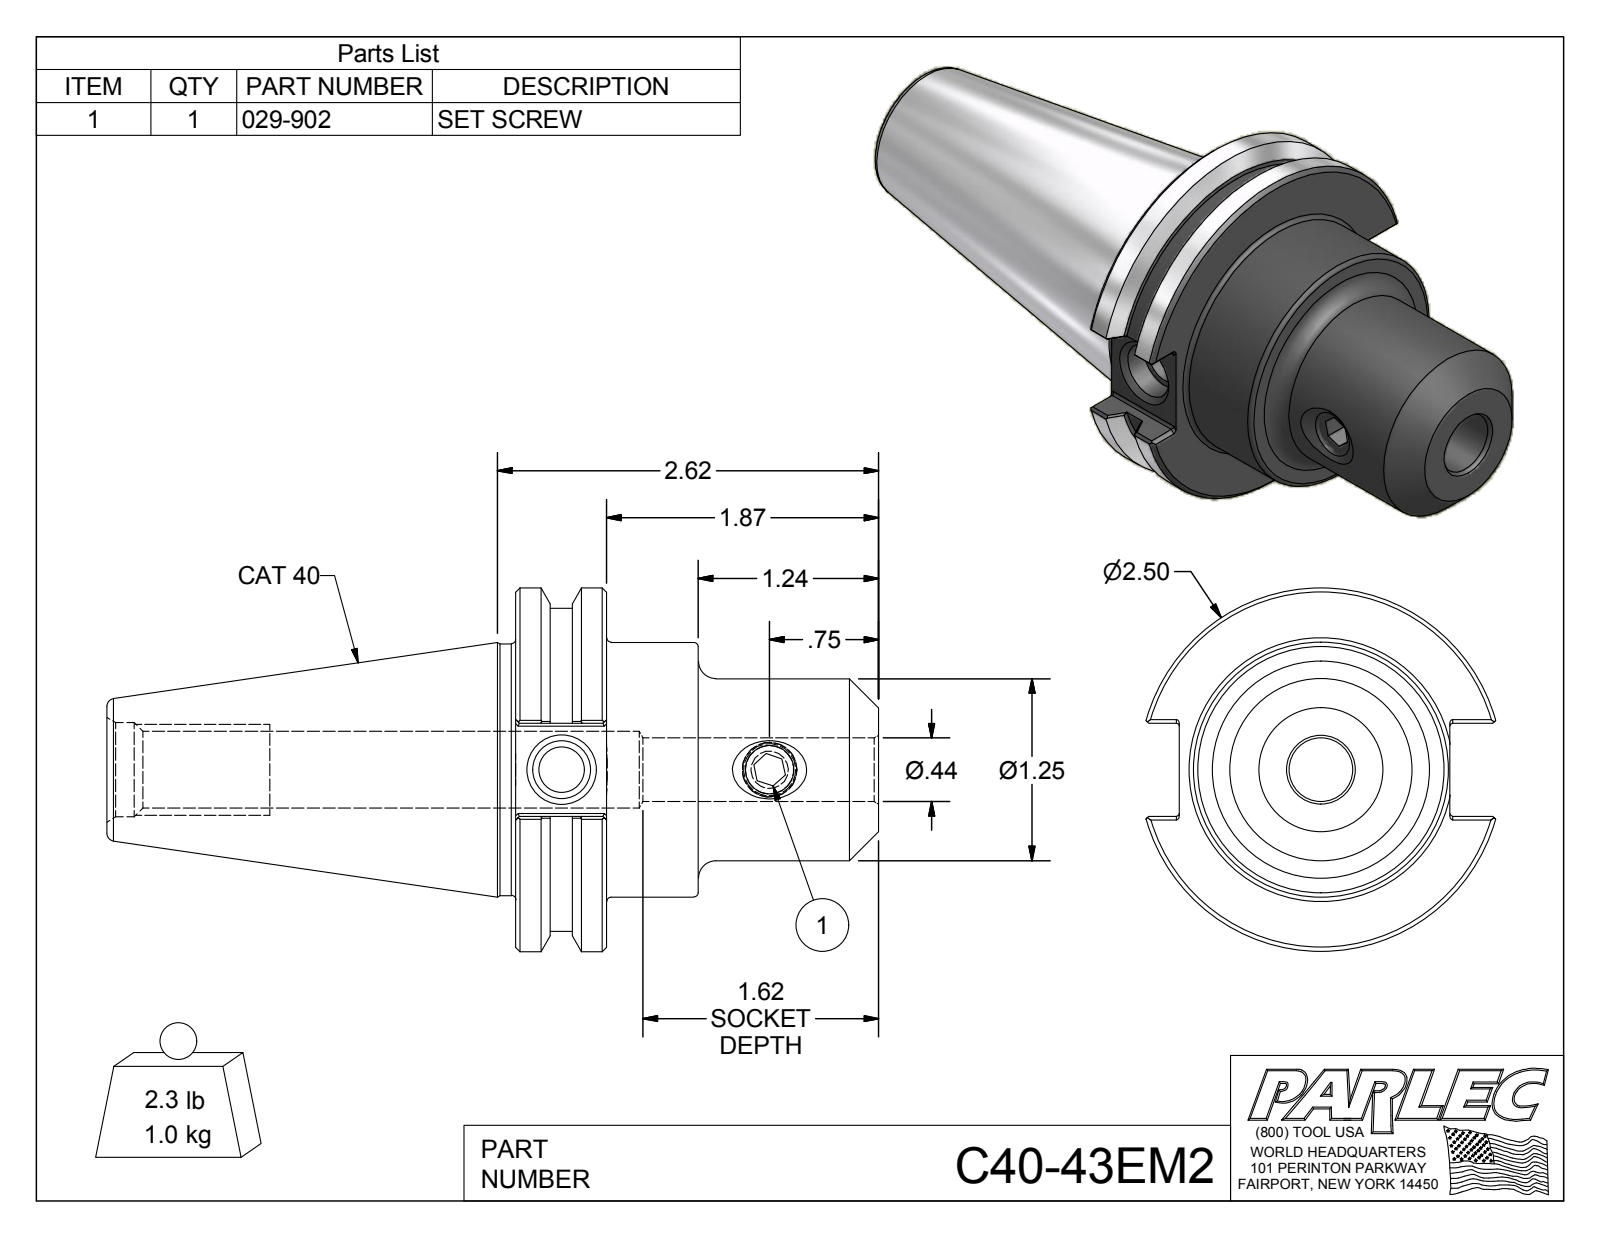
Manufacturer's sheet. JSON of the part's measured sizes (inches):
{"part_name": "C40-43EM2; C40-43EM2-1; 029-902", "step_written_by": "Autodesk Inventor 2012 (AUTOMOTIVE_DESIGN)", "units": "inches", "bodies": {"solids": 2, "faces": 104, "planar": 41, "cylindrical": 29, "other": 34}, "overall_size": [5.307, 2.5, 2.406], "volume_in3": 8.772, "surface_area_in2": 42.66, "round_holes": [[0.315, 1], [0.332, 1], [0.399, 1], [0.437, 1], [0.527, 1], [0.648, 1]], "round_bosses_or_shafts": [[2.5, 1], [2.219, 1], [1.75, 1], [1.73, 1], [1.25, 1], [0.375, 1]], "partial_cylinders_radius": [[0.02, 12]], "face_to_face_distances": [0.625, 1.255, 0.63, 2.495, 1.87, 1.24, 0.64, 0.236, 1.86, 2.812], "hole_center_spacings": [1.43]}
